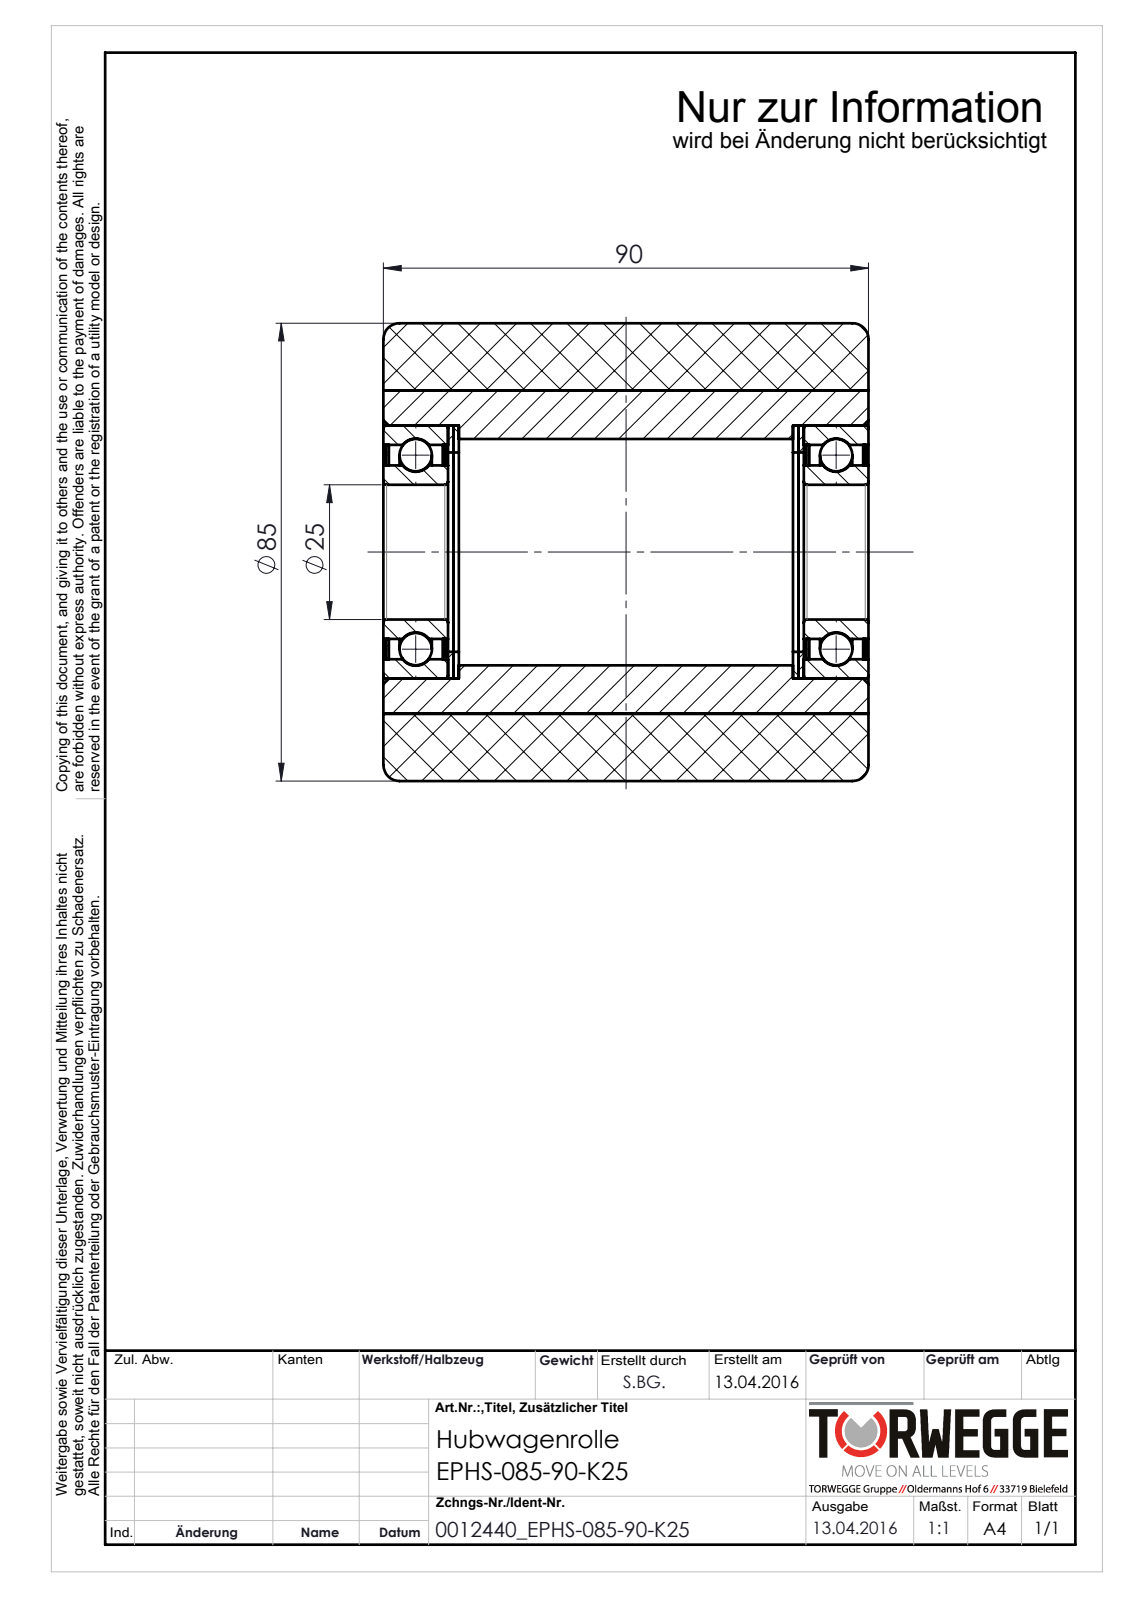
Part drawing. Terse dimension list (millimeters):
name: 0012440_EPHS-085-90-K25
written by: SolidWorks 2016 (AUTOMOTIVE_DESIGN)
unit: mm
bodies: 16 solids, 158 faces (30 planar, 68 cylindrical, 60 other)
size: 90 × 85 × 85
volume: 402 553 mm³; area: 106 559 mm²
holes: 1× ⌀25, 1× ⌀32.2, 1× ⌀37, 1× ⌀39.8, 1× ⌀42, 1× ⌀60
bosses: 1× ⌀85, 1× ⌀47
face distances: 1, 78, 90, 12, 0.5, 13, 77, 65, 64, 76
